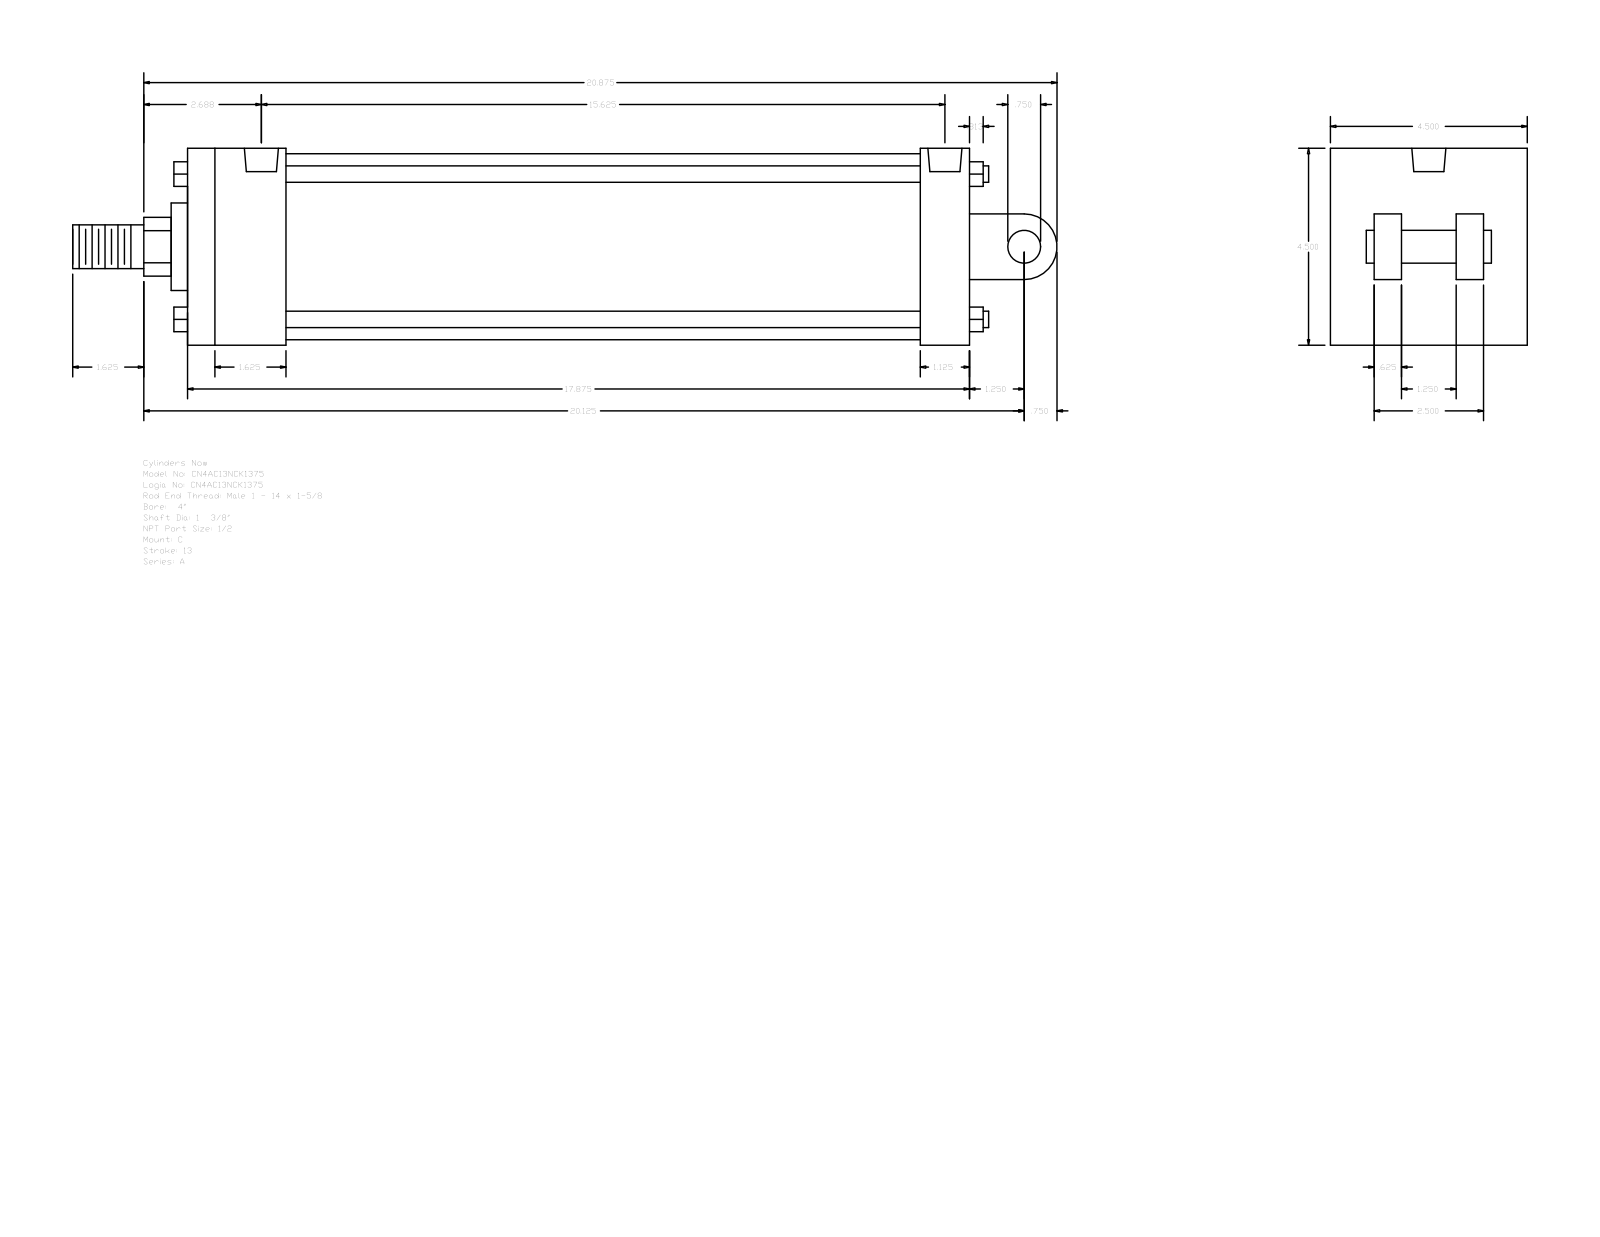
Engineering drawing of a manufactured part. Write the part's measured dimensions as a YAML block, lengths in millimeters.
part_name: "A_C__0400_1.375"
step_written_by: "GSSL Pune (CONFIG_CONTROL_DESIGN)"
units: millimeters
bodies: {solids: 0, faces: 135, planar: 102, cylindrical: 33, other: 0}
overall_size: [571.5, 114.3, 114.3]
round_holes:
  - {diameter: 8.73, count: 4}
  - {diameter: 19.77, count: 2}
round_bosses_or_shafts:
  - {diameter: 9.53, count: 4}
  - {diameter: 107.95, count: 1}
  - {diameter: 50.8, count: 1}
  - {diameter: 34.92, count: 1}
  - {diameter: 25.4, count: 1}
  - {diameter: 19.05, count: 1}
partial_cylinders:
  - {radius: 17.06, count: 1}
  - {radius: 19.05, count: 1}
face_to_face_distances: [114.3, 454.03, 57.15, 28.58, 73.03, 425.45, 368.3, 396.88, 25.4, 41.27]
hole_center_spacings: [3.18, 390.52, 393.7, 396.88]
